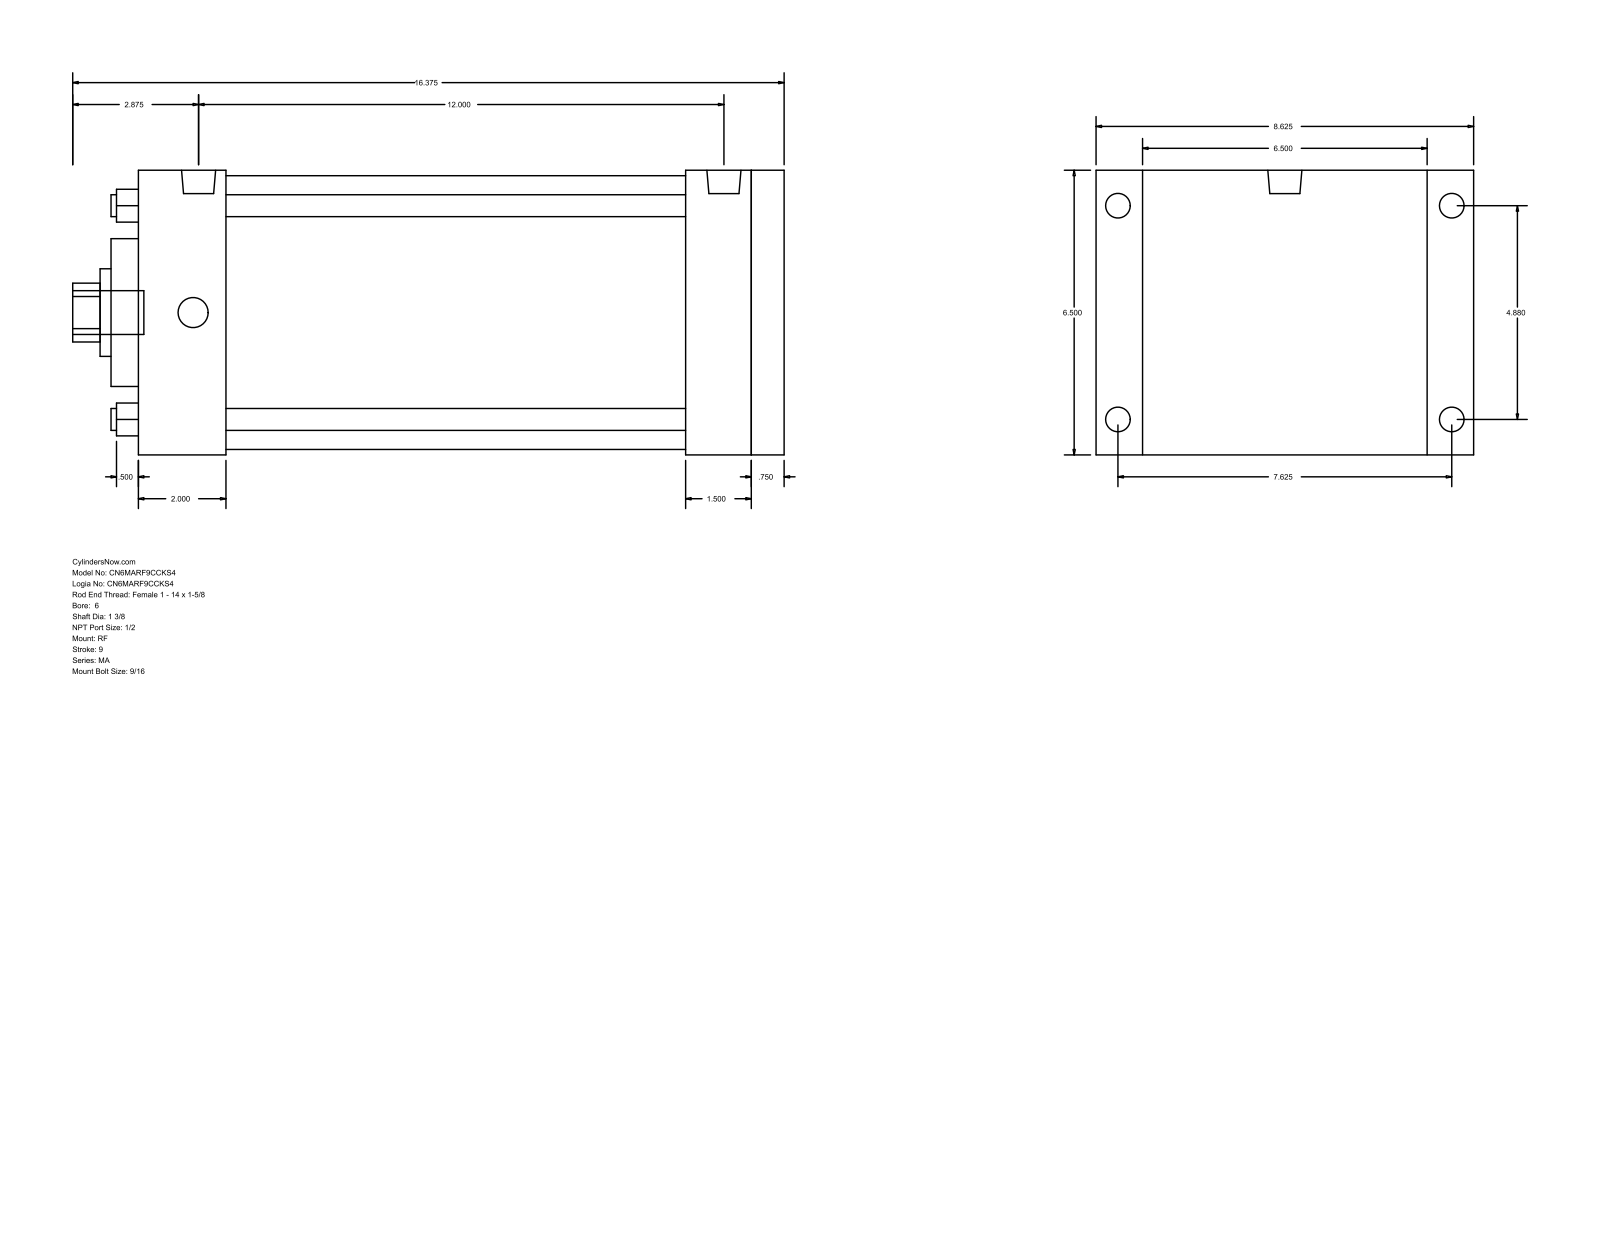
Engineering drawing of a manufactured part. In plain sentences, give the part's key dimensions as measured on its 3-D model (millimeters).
The part is named "MA_RF__0600_1.375". Its 3-D file was written by "GSSL Pune (CONFIG_CONTROL_DESIGN)". It is 0 solids with 94 faces: 65 planar, 29 cylindrical and 0 other. Overall it measures 415.93 by 219.07 by 165.1 millimeters. Round holes: 4 of diameter 12.7, 1 of diameter 34.92, 1 of diameter 50.8, 1 of diameter 85.72, 1 of diameter 158.75. Round bosses or shafts: 4 of diameter 17.46, 4 of diameter 14.29, 2 of diameter 19.77, 1 of diameter 25.4. Partial cylindrical surfaces (rounded edges, fillets, slot ends): 1 of radius 17.06. The main face-to-face distances are 165.1, 377.83, 19.05, 358.78, 50.8, 307.98, 327.03, 320.67, 269.87, 38.11. The hole center spacings are 87.65, 123.96, 175.31.
